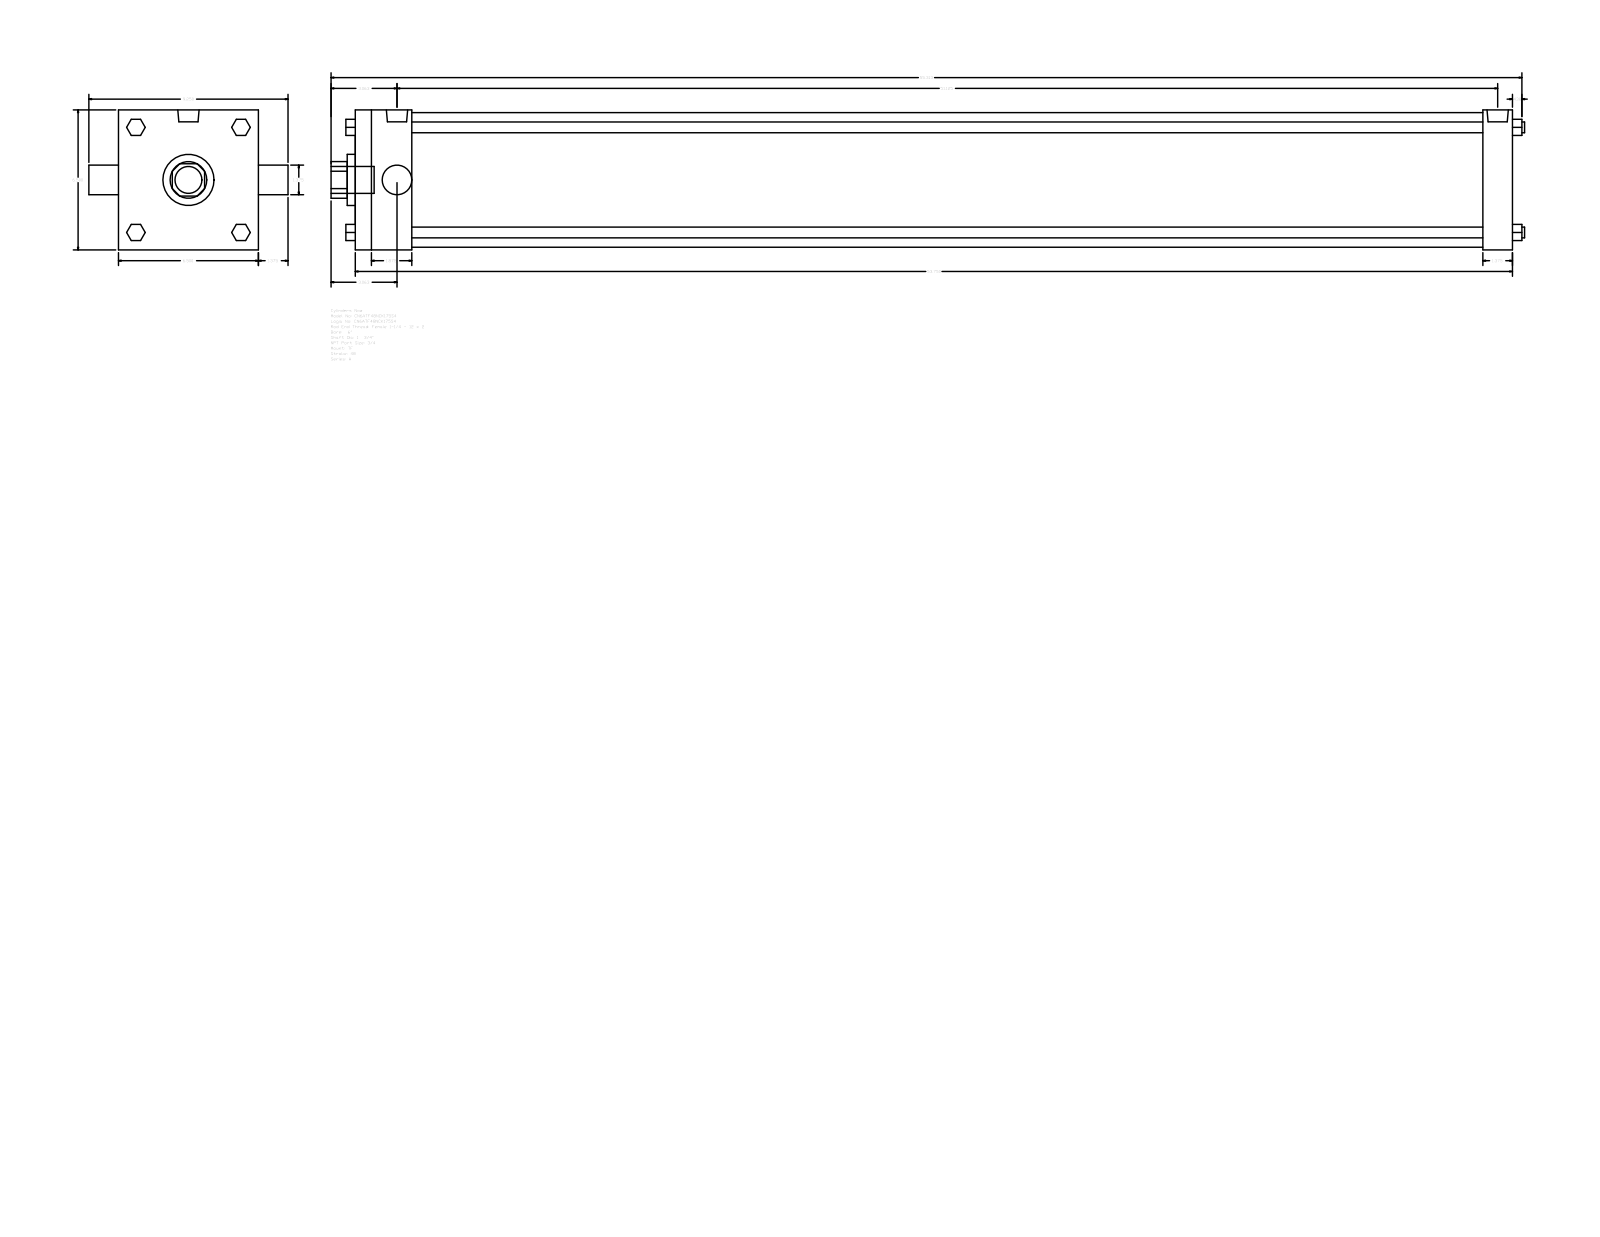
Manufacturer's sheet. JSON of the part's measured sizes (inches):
{"part_name": "A_TF__0600_1.75", "step_written_by": "GSSL Pune (CONFIG_CONTROL_DESIGN)", "units": "inches", "bodies": {"solids": 0, "faces": 120, "planar": 92, "cylindrical": 28, "other": 0}, "overall_size": [55.437, 9.25, 6.5], "round_holes": [[1.375, 1], [1.75, 1], [2.375, 1], [6.25, 1]], "round_bosses_or_shafts": [[0.5, 4], [0.594, 3], [0.989, 2], [1.25, 1]], "partial_cylinders_radius": [[0.852, 1]], "face_to_face_distances": [6.5, 53.75, 2.625, 51.125, 52.375, 49.75, 1.375, 0.75, 1.375, 2.44]}
